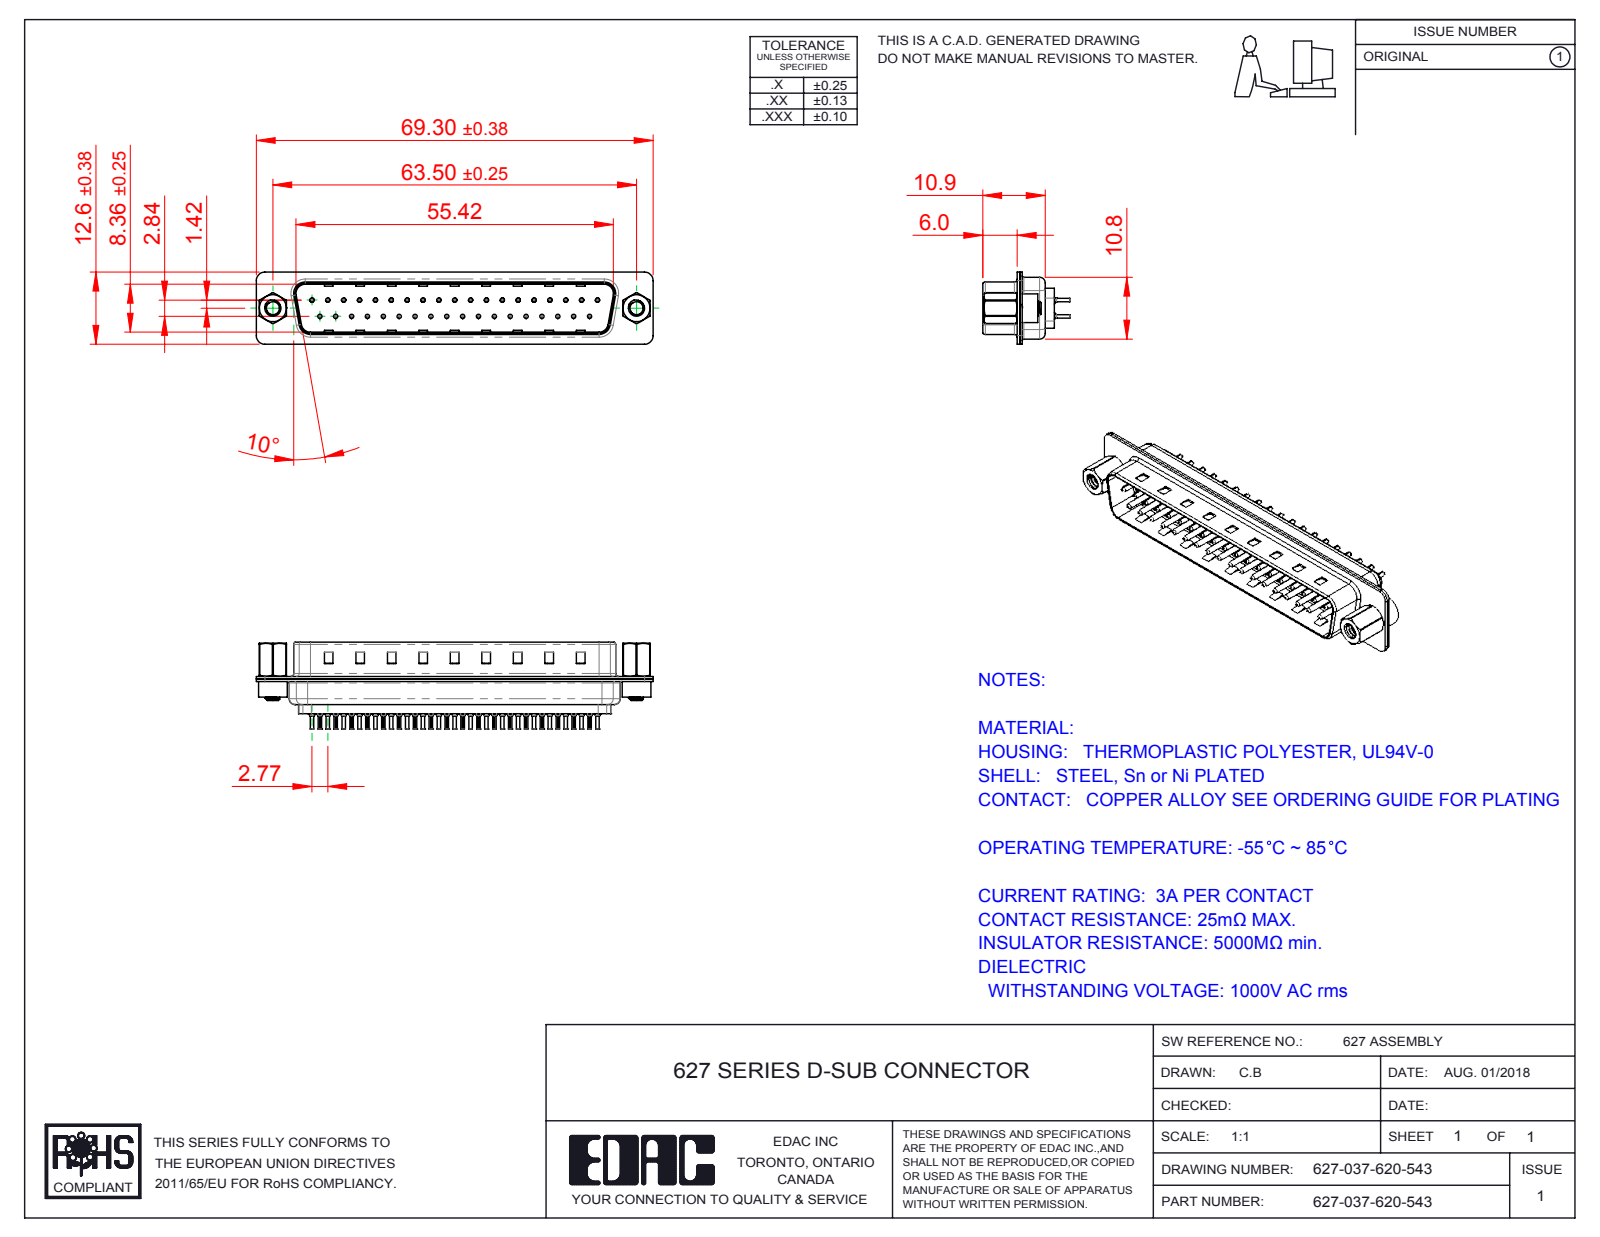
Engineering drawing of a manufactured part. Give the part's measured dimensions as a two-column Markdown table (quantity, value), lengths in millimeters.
| quantity | value |
| --- | --- |
| part name | 627 4-40 Hex Standoff; 627 Contact Row 2_20L; 627-037-620-543; 627 Shell Rear_37 Contacts (+4 more) |
| STEP written by | SolidWorks 2016 (CONFIG_CONTROL_DESIGN) |
| units | millimeters |
| bodies | 44 solids, 4164 faces (1113 planar, 1582 cylindrical, 1469 other) |
| overall size | 69.3 × 15.2 × 12.6 |
| volume | 3 897 mm³ |
| surface area | 10 946 mm² |
| round holes (diameter × count) | 0.2 × 37, 0.35 × 37, 1.1 × 37, 1.6 × 37, 2.26 × 2, 2.29 × 2, 4 × 2, 4.8 × 2 |
| round bosses / shafts (diameter × count) | 2 × 37, 1.5 × 37, 0.75 × 37, 0.6 × 37, 5 × 2, 4.9 × 2, 2.79 × 2 |
| partial cylindrical surfaces (radius × count) | 0.1 × 74, 1.5 × 16, 2 × 12, 0.5 × 8, 1.6 × 8, 0.25 × 4, 0.6 × 4, 0.65 × 4 |
| main face-to-face distances | 0.4, 0.82, 9.58, 0.45, 8.76, 0.9, 1.5, 1.4, 6.05, 6.5 |
| hole center spacings | 3.16, 2.77, 5.54, 8.31, 5.04, 10.1, 11.08, 12.78 |
